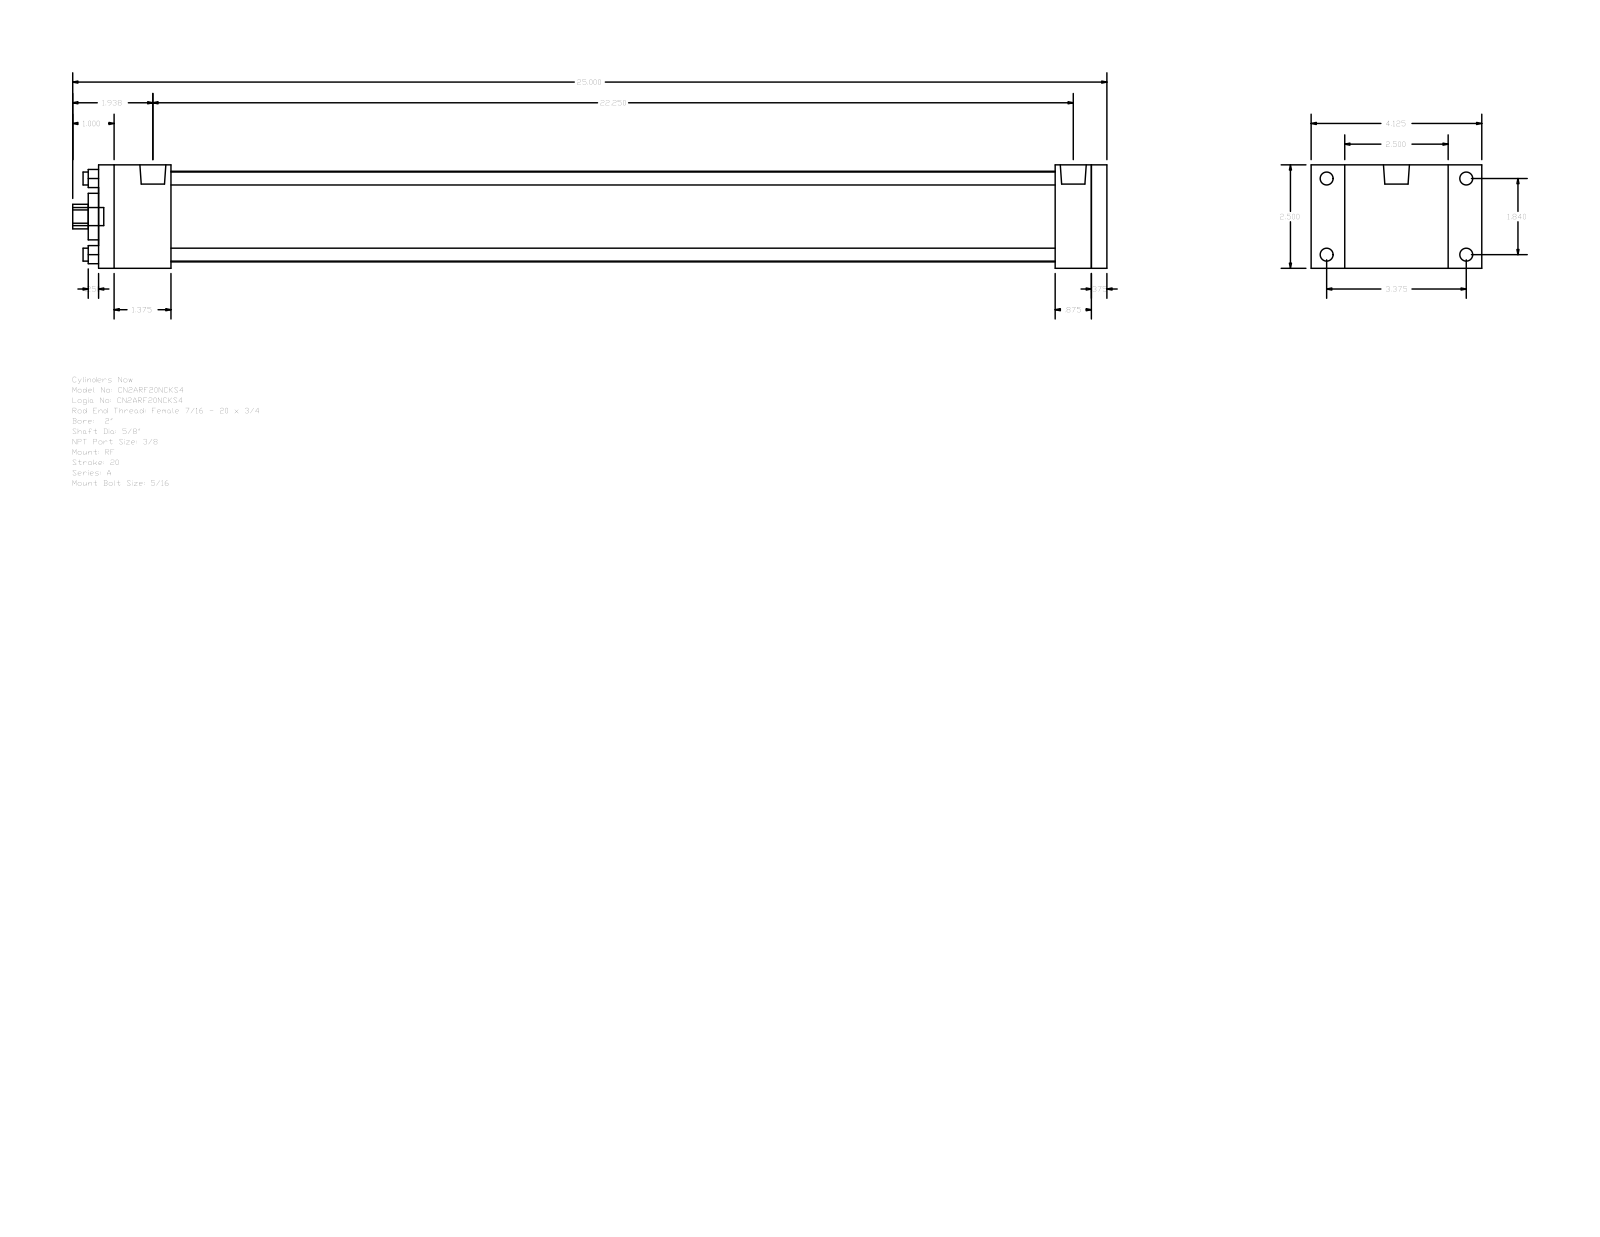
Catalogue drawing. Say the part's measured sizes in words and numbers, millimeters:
The part is named "A_RF__0200_0.625". Its 3-D file was written by "GSSL Pune (CONFIG_CONTROL_DESIGN)". It is 0 solids with 92 faces: 64 planar, 28 cylindrical and 0 other. Overall it measures 635 by 104.78 by 63.5 millimeters. Round holes: 4 of diameter 7.94, 1 of diameter 15.88, 1 of diameter 28.57, 1 of diameter 55.63. Round bosses or shafts: 4 of diameter 7.94, 4 of diameter 5.56, 2 of diameter 15.93, 1 of diameter 11.11. Partial cylindrical surfaces (rounded edges, fillets, slot ends): 1 of radius 7.54. The main face-to-face distances are 63.5, 619.12, 9.52, 609.6, 44.45, 565.15, 574.67, 587.37, 542.92, 22.23. The hole center spacings are 33.05, 46.74, 66.1.
